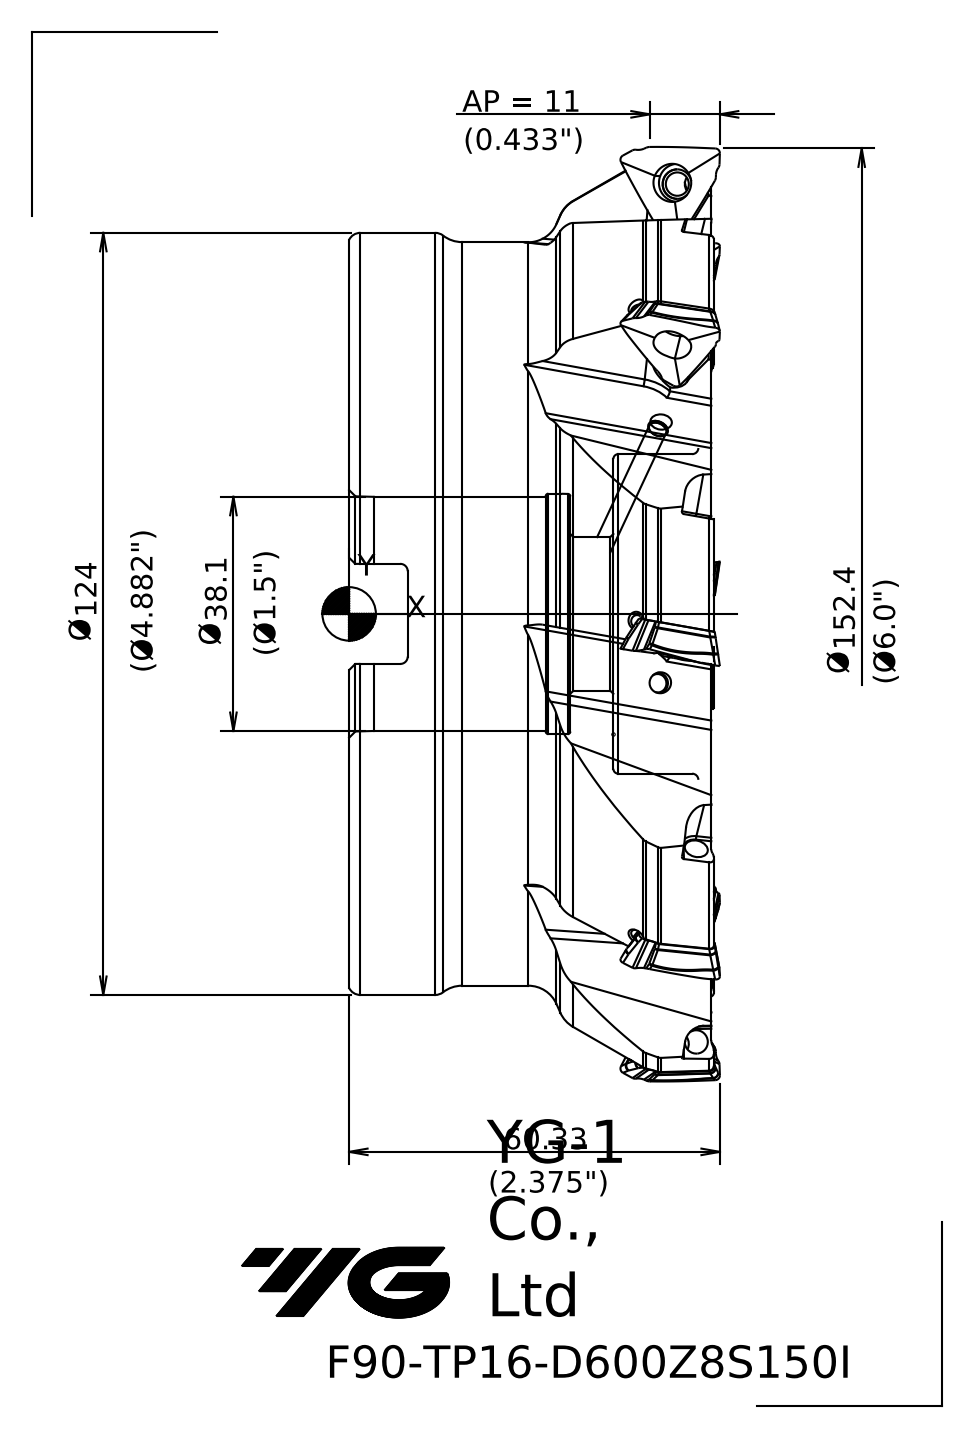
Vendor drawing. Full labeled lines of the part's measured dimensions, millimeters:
Part name (STEP PRODUCT): 1022C79461C3qzz8
STEP written by: SIEMENS PLM Software NX 10.0 (AP203_CONFIGURATION_CONTROLLED_3D_DESIGN_OF_MECHANICAL_PARTS_AND_ASSEMBLIES_MIM_LF)
Units: millimetres
Bodies: 1 solid, 77 faces (18 planar, 10 cylindrical, 49 other)
Overall size (bounding box): 152.54 × 152.54 × 60.33
Volume: 700 224 mm³ · Surface area: 85 026 mm²
Round holes (diameter × count): ⌀25 ×1, ⌀38.1 ×1, ⌀39.1 ×1, ⌀52 ×1
Round bosses / shafts (diameter × count): ⌀124 ×1, ⌀121 ×1
Partial cylindrical surfaces — rounded edges, fillets, slot ends (radius × count): R1.2 ×2
Main face-to-face distances: 58.93, 2.1, 56.83, 15.93, 13.83, 43, 49.39, 47.29, 33.46, 9.54
